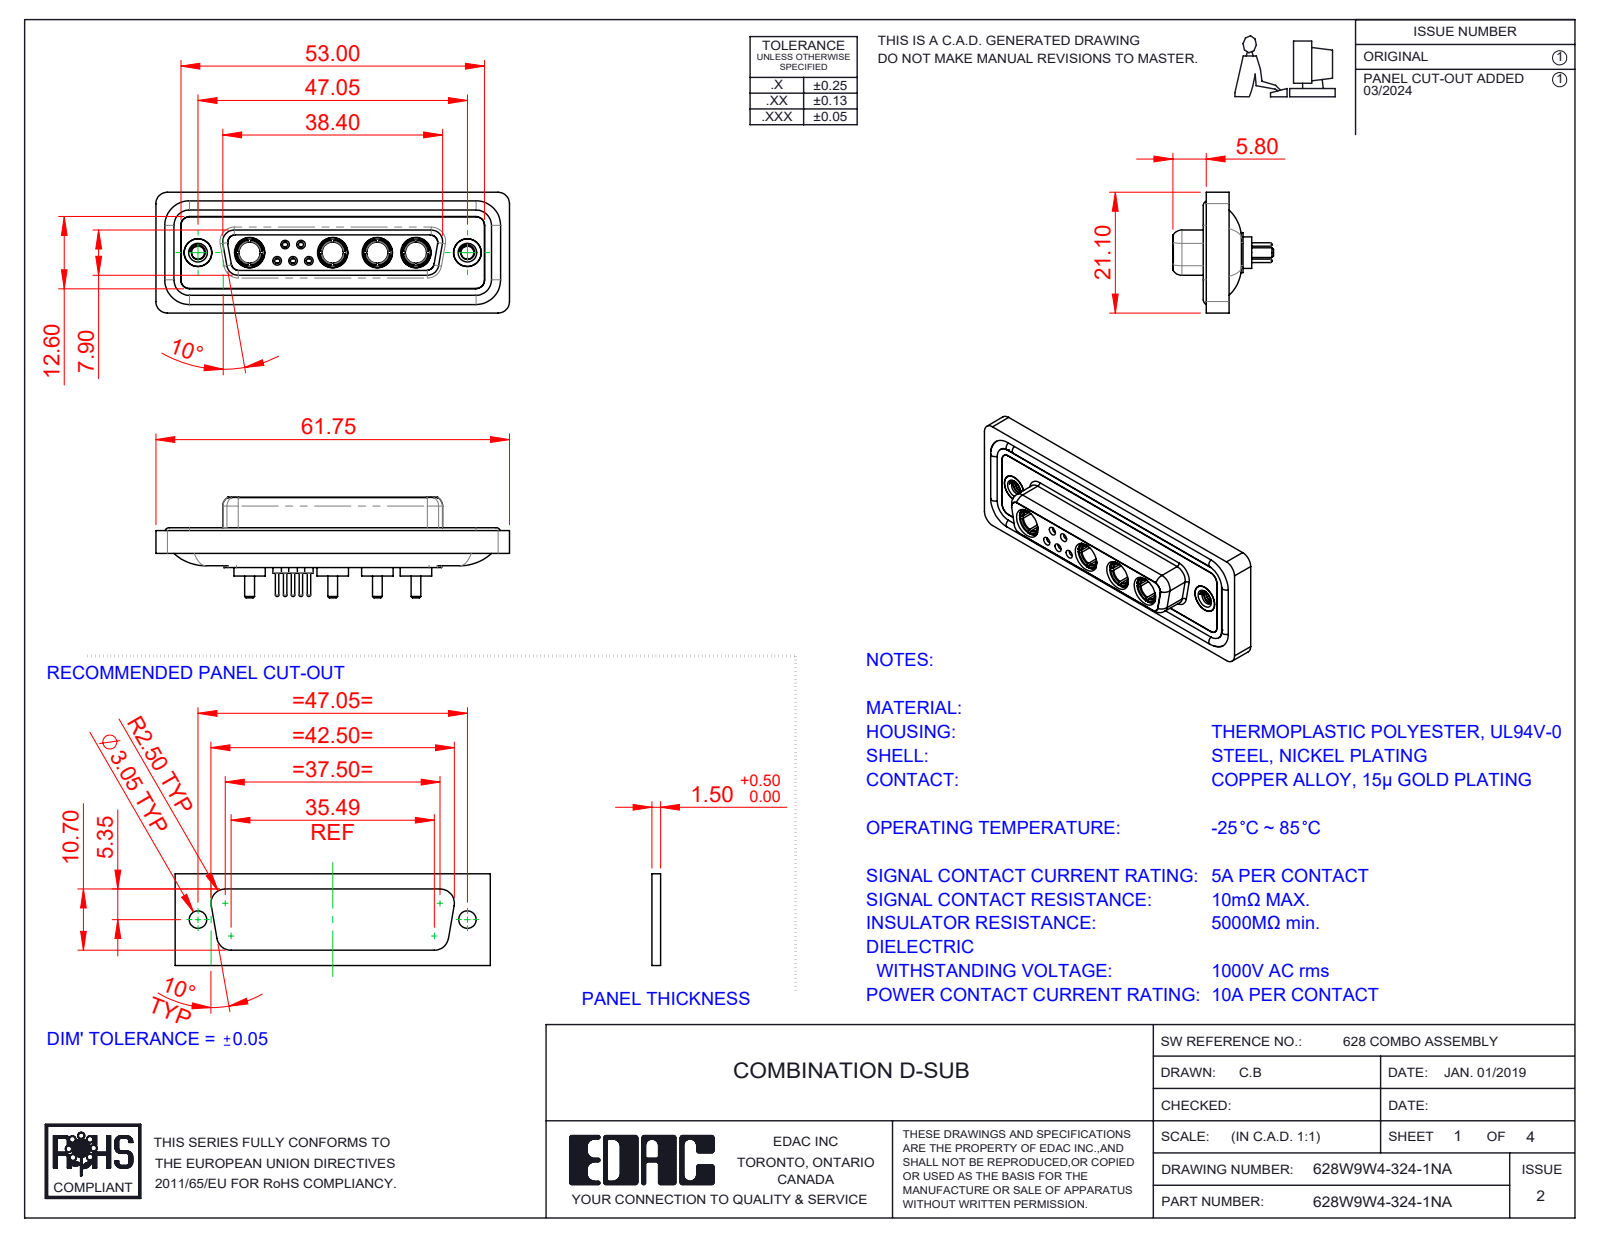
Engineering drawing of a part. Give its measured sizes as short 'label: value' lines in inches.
name: 628Combo Housing_9W4; 628Combo Shell Front_25 Contacts; 628Combo Threaded Rivet_A; Power Socket_10A S (+5 more)
written by: SolidWorks 2023 (CONFIG_CONTROL_DESIGN)
unit: in
bodies: 20 solids, 955 faces (296 planar, 377 cylindrical, 282 other)
size: 2.431 × 0.831 × 0.691
volume: 0.498 in³; area: 20.94 in²
holes: 6× ⌀0.191, 5× ⌀0.035, 5× ⌀0.043, 5× ⌀0.059, 5× ⌀0.079, 4× ⌀0.146, 4× ⌀0.209, 3× ⌀0.063, 2× ⌀0.067, 2× ⌀0.089, 2× ⌀0.157, 2× ⌀0.159
bosses: 6× ⌀0.063, 5× ⌀0.087, 5× ⌀0.024, 4× ⌀0.217, 4× ⌀0.205, 4× ⌀0.195, 4× ⌀0.187, 4× ⌀0.148
rounds: 22× R0.059, 18× R0.079, 8× R0.053, 8× R0.063, 4× R0.01, 4× R0.02, 4× R0.024, 4× R0.026
face distances: 0.016, 0.071, 0.293, 0.222, 0.02, 0.278, 0.26, 0.063, 0.043, 0.114
hole spacings: 0.124, 0.109, 0.198, 0.109, 0.173, 0.198, 0.218, 0.226
